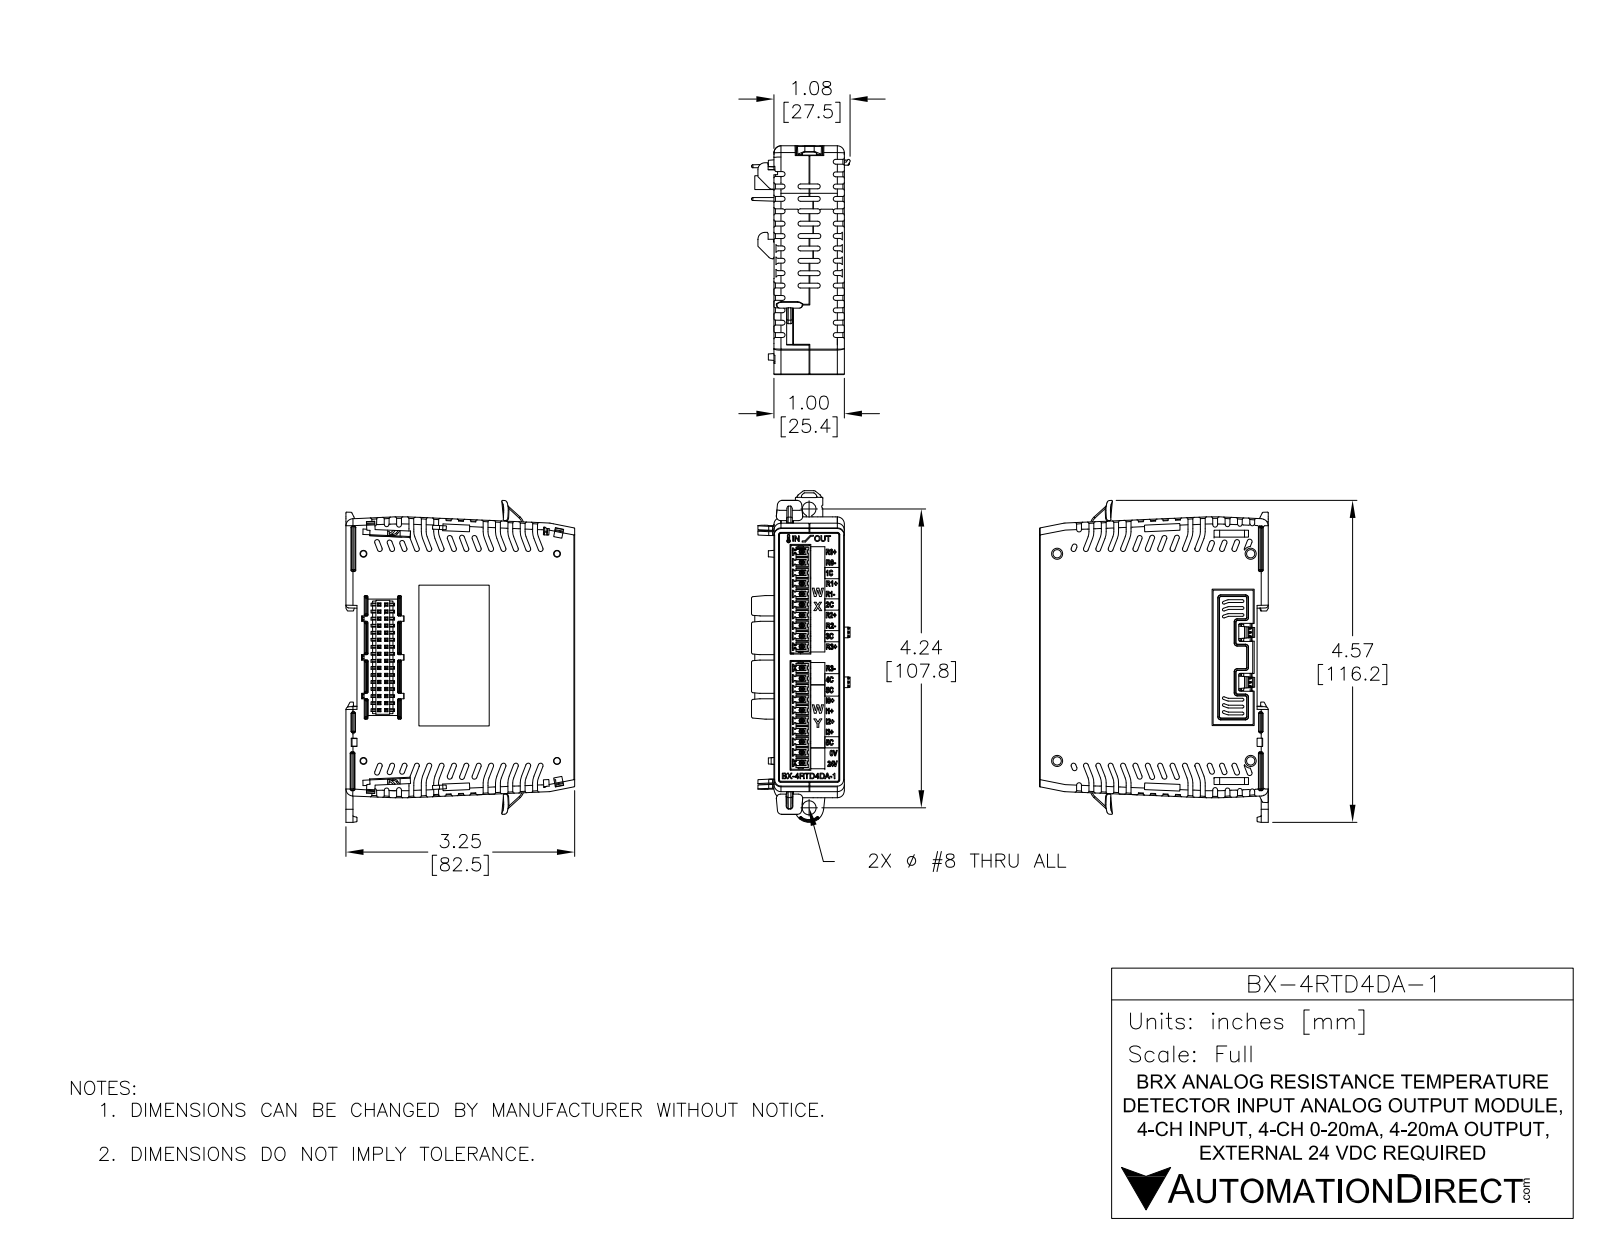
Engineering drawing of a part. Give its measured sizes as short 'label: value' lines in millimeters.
name: BX-4RTD4DA-1
written by: SolidWorks 2017 (AUTOMOTIVE_DESIGN)
unit: mm
bodies: 11 solids, 4966 faces (3507 planar, 636 cylindrical, 823 other)
size: 116.5 × 82.6 × 35.6
volume: 155 000 mm³; area: 57 590 mm²
holes: 8× ⌀0.4, 2× ⌀0.4, 2× ⌀3, 2× ⌀3, 1× ⌀1, 1× ⌀5.1
bosses: 2× ⌀2.8, 2× ⌀1.5, 1× ⌀1.8, 1× ⌀1.1, 1× ⌀0.9
rounds: 109× R0.5, 103× R0.2, 48× R0.1, 20× R1.6, 16× R0.3, 16× R0.4, 14× R0.3, 12× R0.2
face distances: 25.4, 21.2, 4.2, 77.5, 5.3, 15.9, 20.1, 77.8, 52.1, 25.7
hole spacings: 3.8, 7.6, 11.4, 15.2, 19.1, 41.9, 22.9, 38.1
